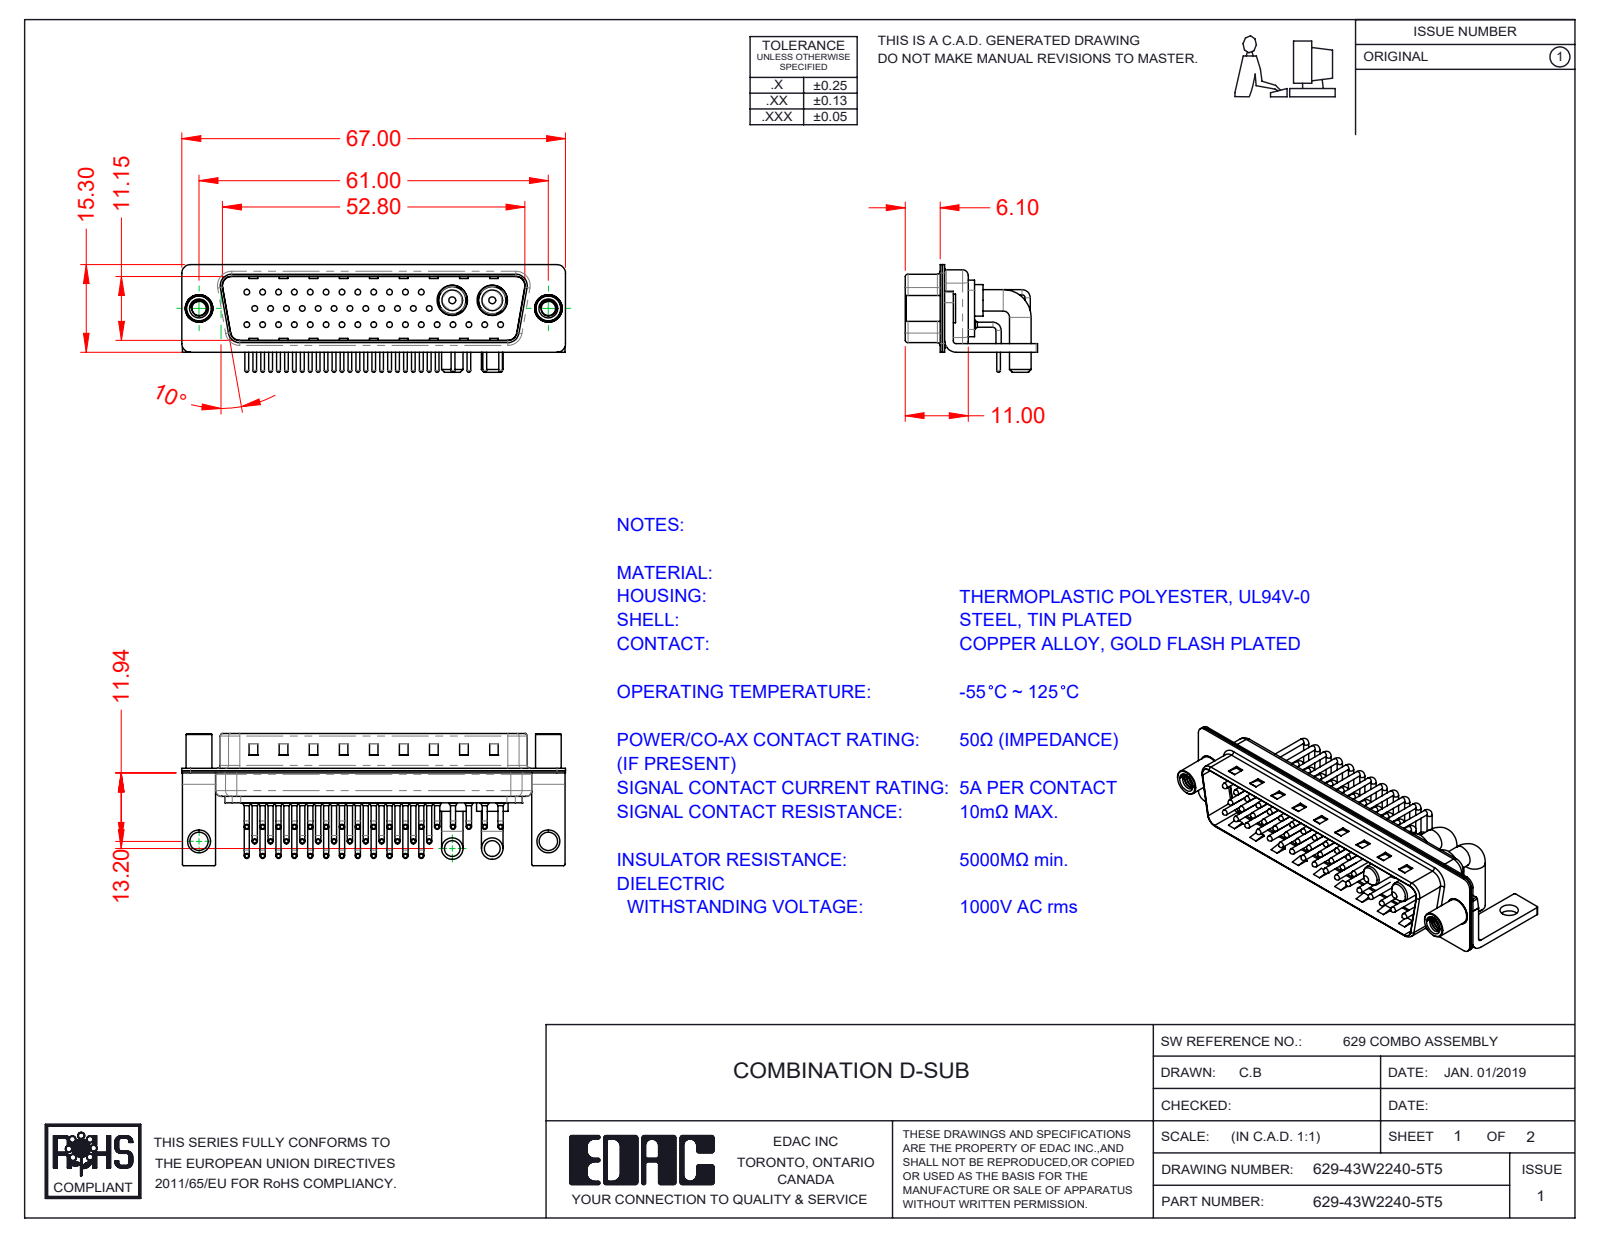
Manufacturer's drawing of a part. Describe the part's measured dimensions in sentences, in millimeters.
The part is named "629Combo Stabilizer Bracket_50 Contacts; 629Combo Contact Row 2_50 Contacts; 629Combo Housing_43W2; 629Combo Threaded Standoff_D (+6 more)". Its 3-D file was written by "SolidWorks 2020 (CONFIG_CONTROL_DESIGN)". It is 52 solids with 5106 faces: 2869 planar, 1731 cylindrical and 506 other. Overall it measures 67 by 23.1 by 18.8 millimeters. Its volume is 5 837 cubic millimeters and its surface area 13 730 square millimeters. Round holes: 41 of diameter 0.75, 41 of diameter 1.6, 41 of diameter 2, 2 of diameter 2.5, 2 of diameter 3.2, 2 of diameter 4, 2 of diameter 4.8, 2 of diameter 4.85, 2 of diameter 5.3. Round bosses or shafts: 82 of diameter 0.9, 41 of diameter 1.5, 41 of diameter 1, 41 of diameter 0.65, 4 of diameter 3.75, 2 of diameter 5.5, 2 of diameter 5.2, 2 of diameter 5. Partial cylindrical surfaces (rounded edges, fillets, slot ends): 41 of radius 1.01, 16 of radius 0.25, 16 of radius 1.5, 13 of radius 2, 9 of radius 0.5, 8 of radius 1.6, 4 of radius 0.6, 4 of radius 0.65. The main face-to-face distances are 0.4, 1.5, 11.55, 5.6, 5.2, 0.8, 1.9, 4.1, 6, 0.78. The hole center spacings are 2.77, 5.54, 3.16, 8.31, 11.08, 13.85, 16.62, 19.39.
